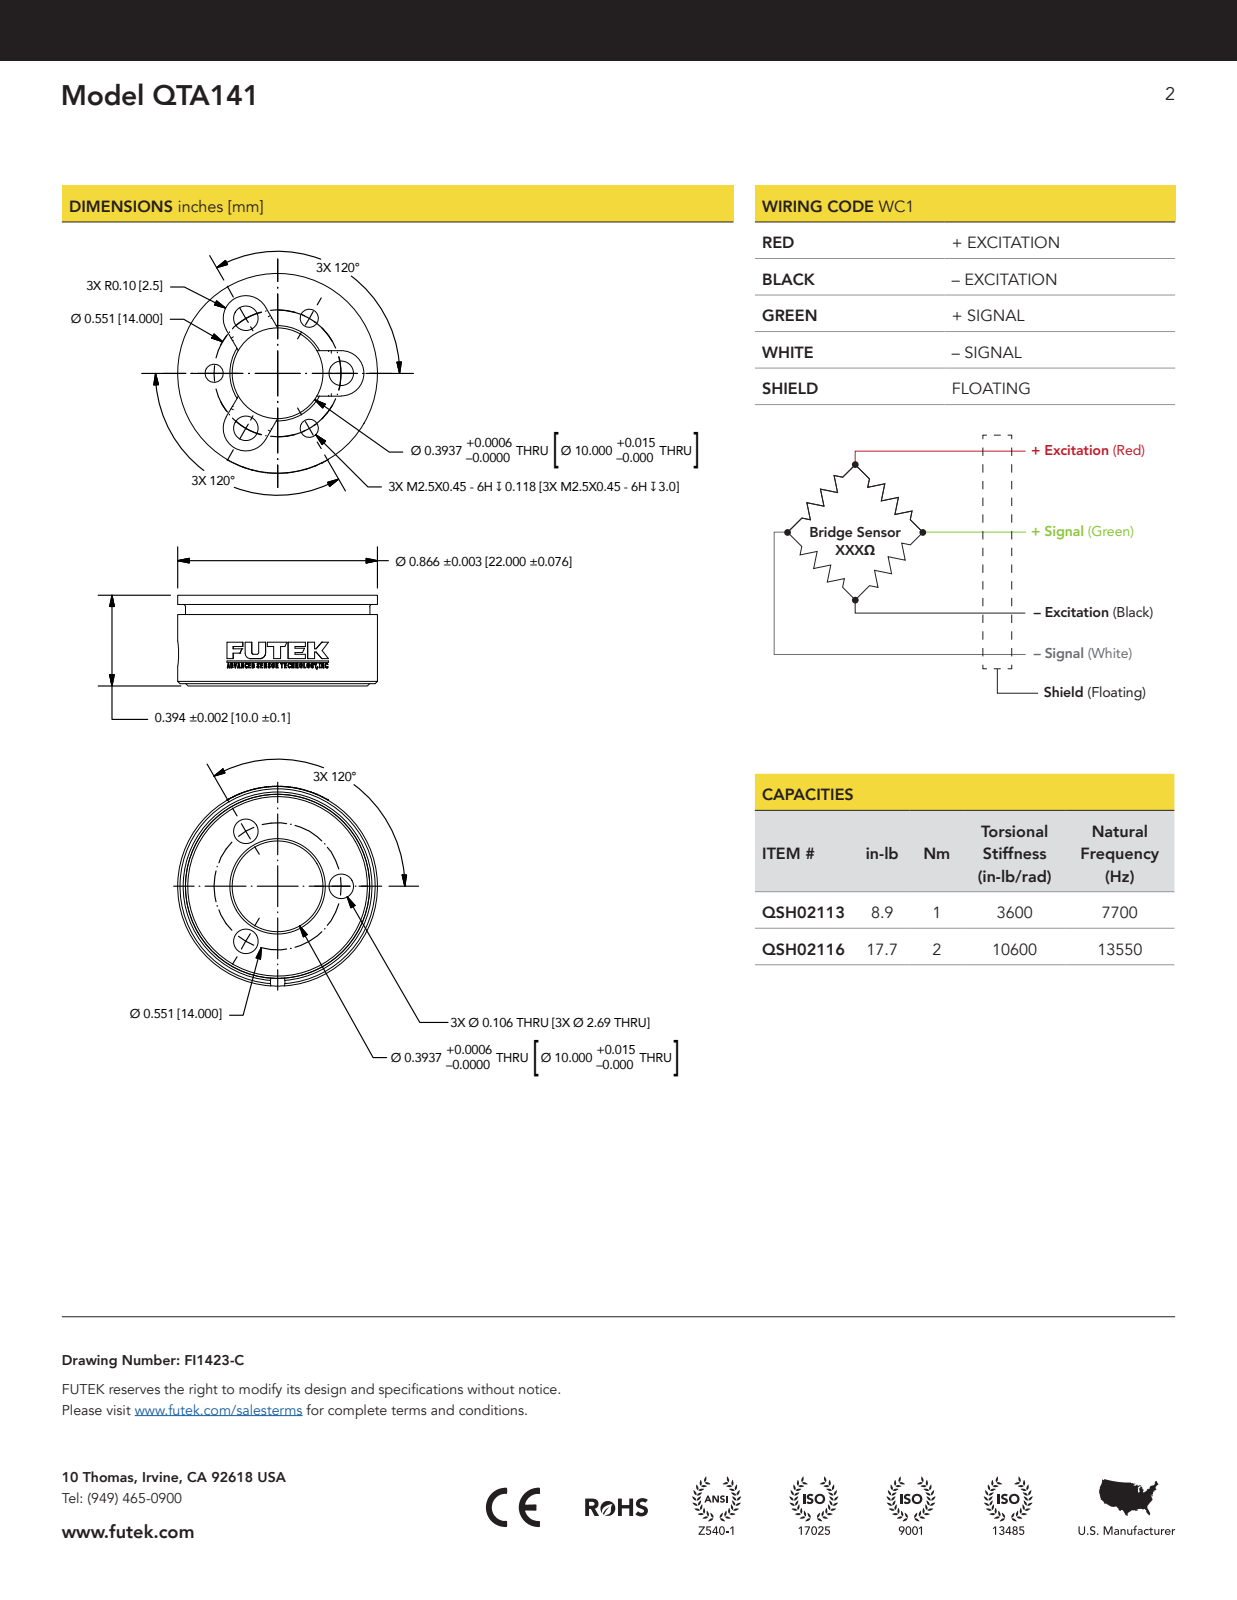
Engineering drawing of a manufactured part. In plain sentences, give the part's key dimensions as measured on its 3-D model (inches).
The part is named "Simple Assembly". Its 3-D file was written by "Autodesk Inventor 2015 (AUTOMOTIVE_DESIGN)". It is 7 solids with 908 faces: 485 planar, 77 cylindrical and 346 other. Overall it measures 6.862 by 0.867 by 0.394 inches. Its volume is 0.126 cubic inches and its surface area 5.647 square inches. Round holes: 3 of diameter 0.079, 3 of diameter 0.106, 1 of diameter 0.094, 1 of diameter 0.394, 1 of diameter 0.798, 1 of diameter 0.825. Round bosses or shafts: 4 of diameter 0.01, 1 of diameter 0.866, 1 of diameter 0.865, 1 of diameter 0.8, 1 of diameter 0.787, 1 of diameter 0.73, 1 of diameter 0.08, 1 of diameter 0.05. Partial cylindrical surfaces (rounded edges, fillets, slot ends): 3 of radius 0.098, 1 of radius 0.031, 1 of radius 0.26, 1 of radius 0.433. The main face-to-face distances are 0.394, 0.08, 0.314, 0.04, 0.274, 0.354, 0.055, 0.369, 0.329, 0.025. The hole center spacings are 0.276, 0.477, 0.551.
